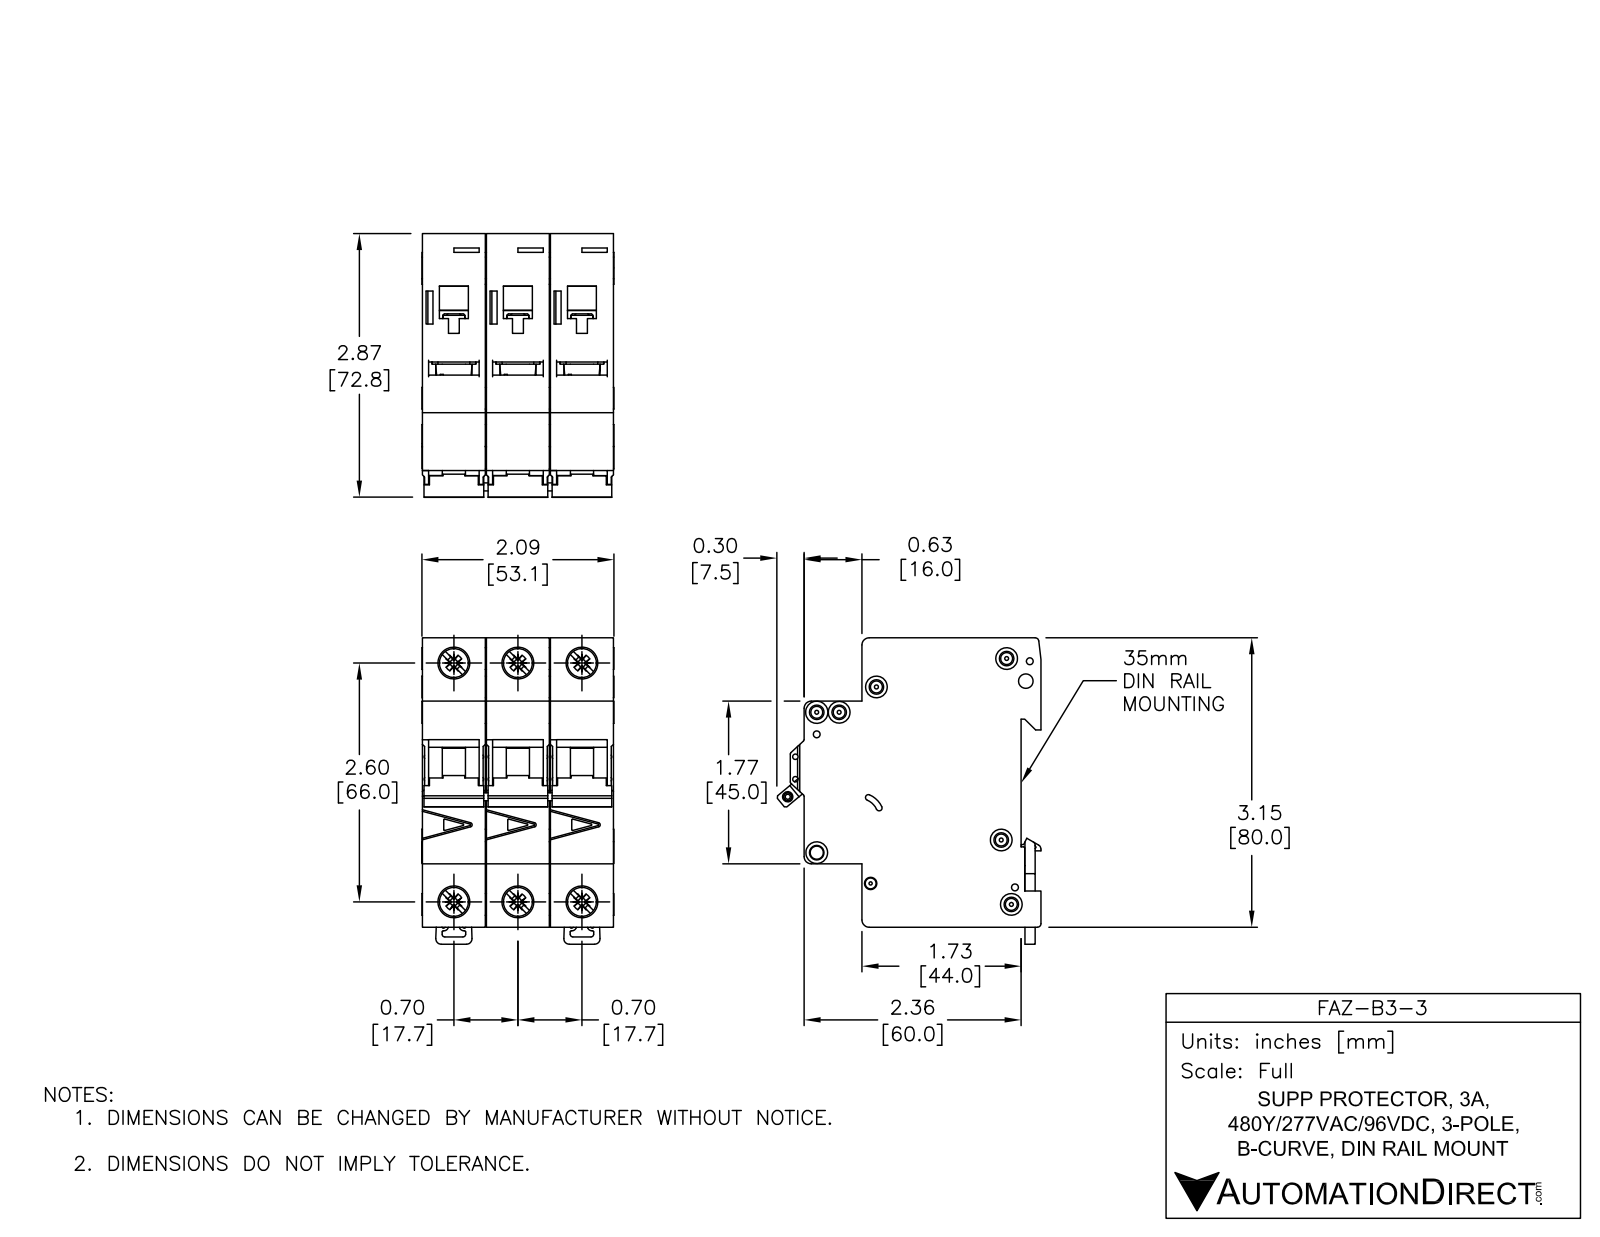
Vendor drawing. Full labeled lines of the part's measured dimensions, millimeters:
Part name (STEP PRODUCT): FAZ-B3-3
STEP written by: SolidWorks 2014 (AUTOMOTIVE_DESIGN)
Units: millimetres
Bodies: 11 solids, 1650 faces (697 planar, 590 cylindrical, 363 other)
Overall size (bounding box): 84.78 × 73.04 × 53.1
Volume: 224 680 mm³ · Surface area: 58 052 mm²
Round holes (diameter × count): ⌀3.6 ×6, ⌀8.2 ×4, ⌀1.9 ×3, ⌀1.09 ×2, ⌀1.5 ×2, ⌀4 ×2, ⌀7.15 ×2, ⌀2.15 ×1, ⌀2.2 ×1, ⌀2.55 ×1, ⌀3.3 ×1, ⌀3.4 ×1
Round bosses / shafts (diameter × count): ⌀6 ×4, ⌀2.5 ×3, ⌀8.2 ×2
Partial cylindrical surfaces — rounded edges, fillets, slot ends (radius × count): R0.25 ×68, R0.5 ×25, R1 ×12, R2 ×12, R0.2 ×11, R1.8 ×3, R0.8 ×2, R3 ×2
Main face-to-face distances: 17.7, 17.5, 35.4, 35.2, 52.9, 17.9, 79.48, 5.5, 49.5, 44
Hole centre spacings: 17.7, 68.33, 66, 6.2, 13.64, 35.4, 74.89, 4.81
